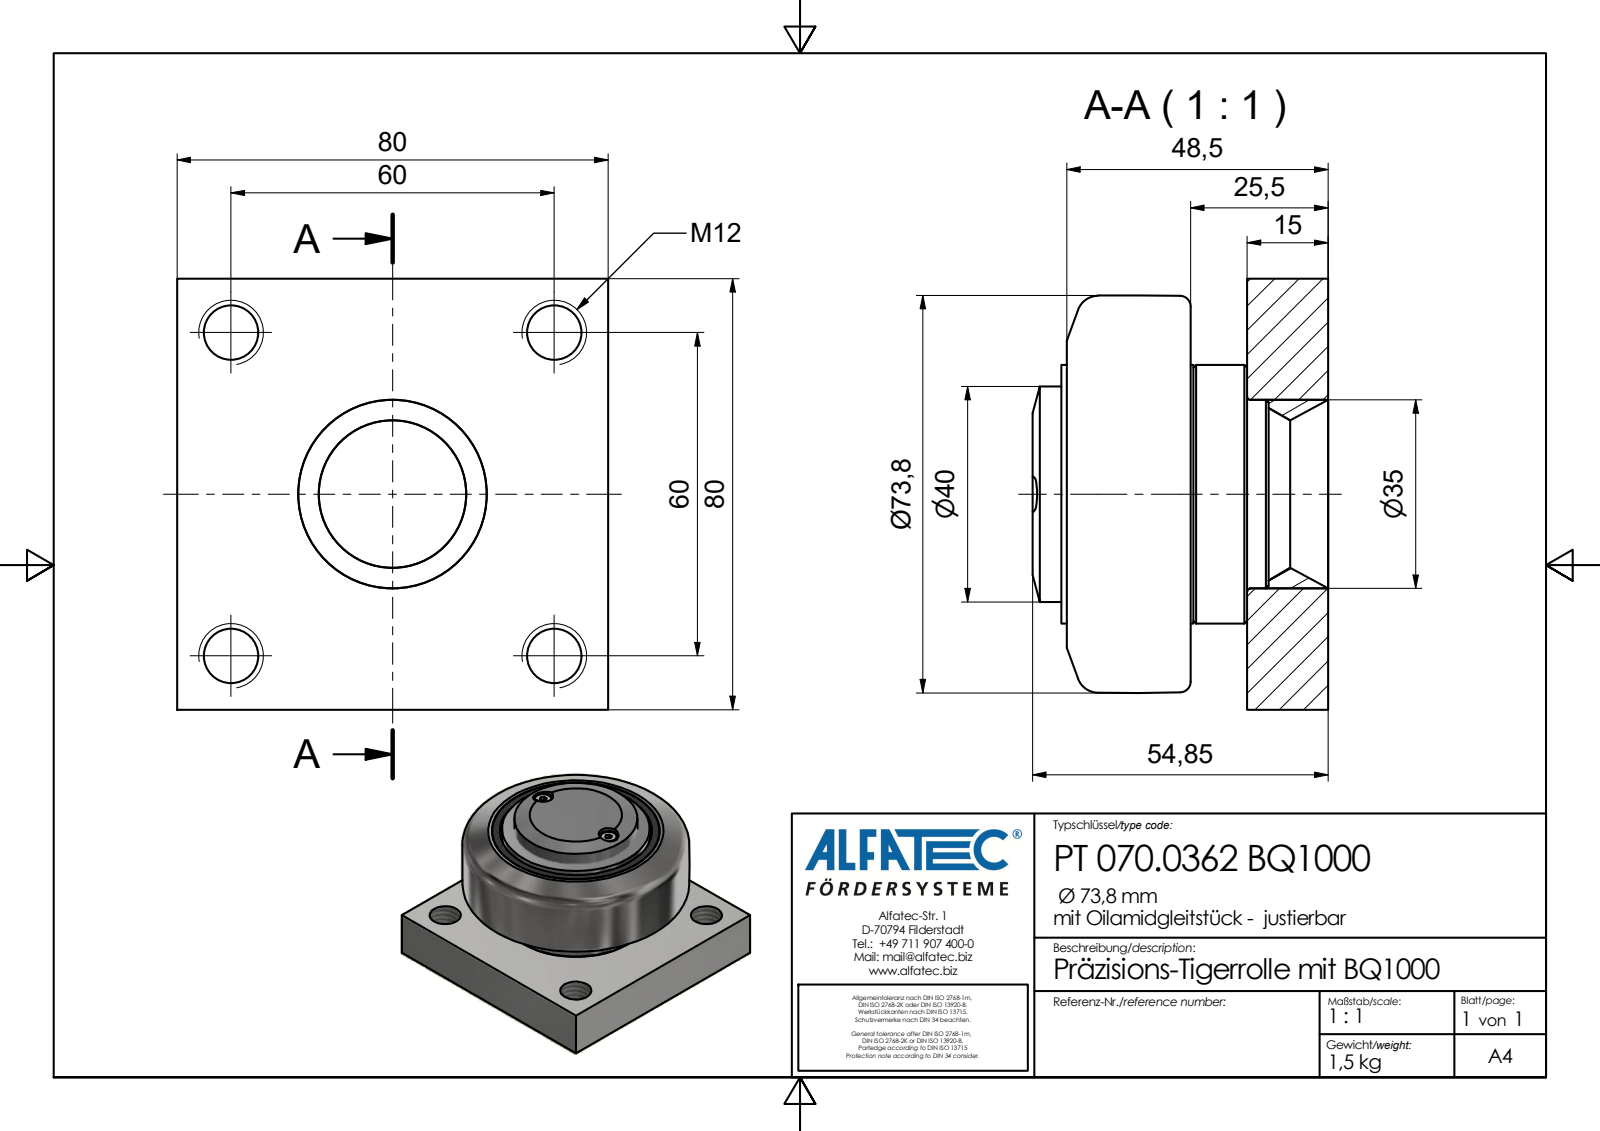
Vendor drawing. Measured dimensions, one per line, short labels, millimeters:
name: PT 070.0362 BQ1000_Kontur
written by: Autodesk Inventor 2020 (AP242_MANAGED_MODEL_BASED_3D_ENGINEERING_MIM_LF)
unit: mm
bodies: 1 solid, 50 faces (28 planar, 12 cylindrical, 10 other)
size: 80 × 80 × 54.85
volume: 207 820 mm³; area: 31 090 mm²
holes: 4× ⌀10.11, 2× ⌀6.5
bosses: 2× ⌀5.35, 1× ⌀48, 1× ⌀40
face distances: 15, 80, 25.5, 10.5, 48.5, 33.5, 23, 54.85, 39.85, 29.35
hole spacings: 33.54, 54.08, 60, 84.85, 30
